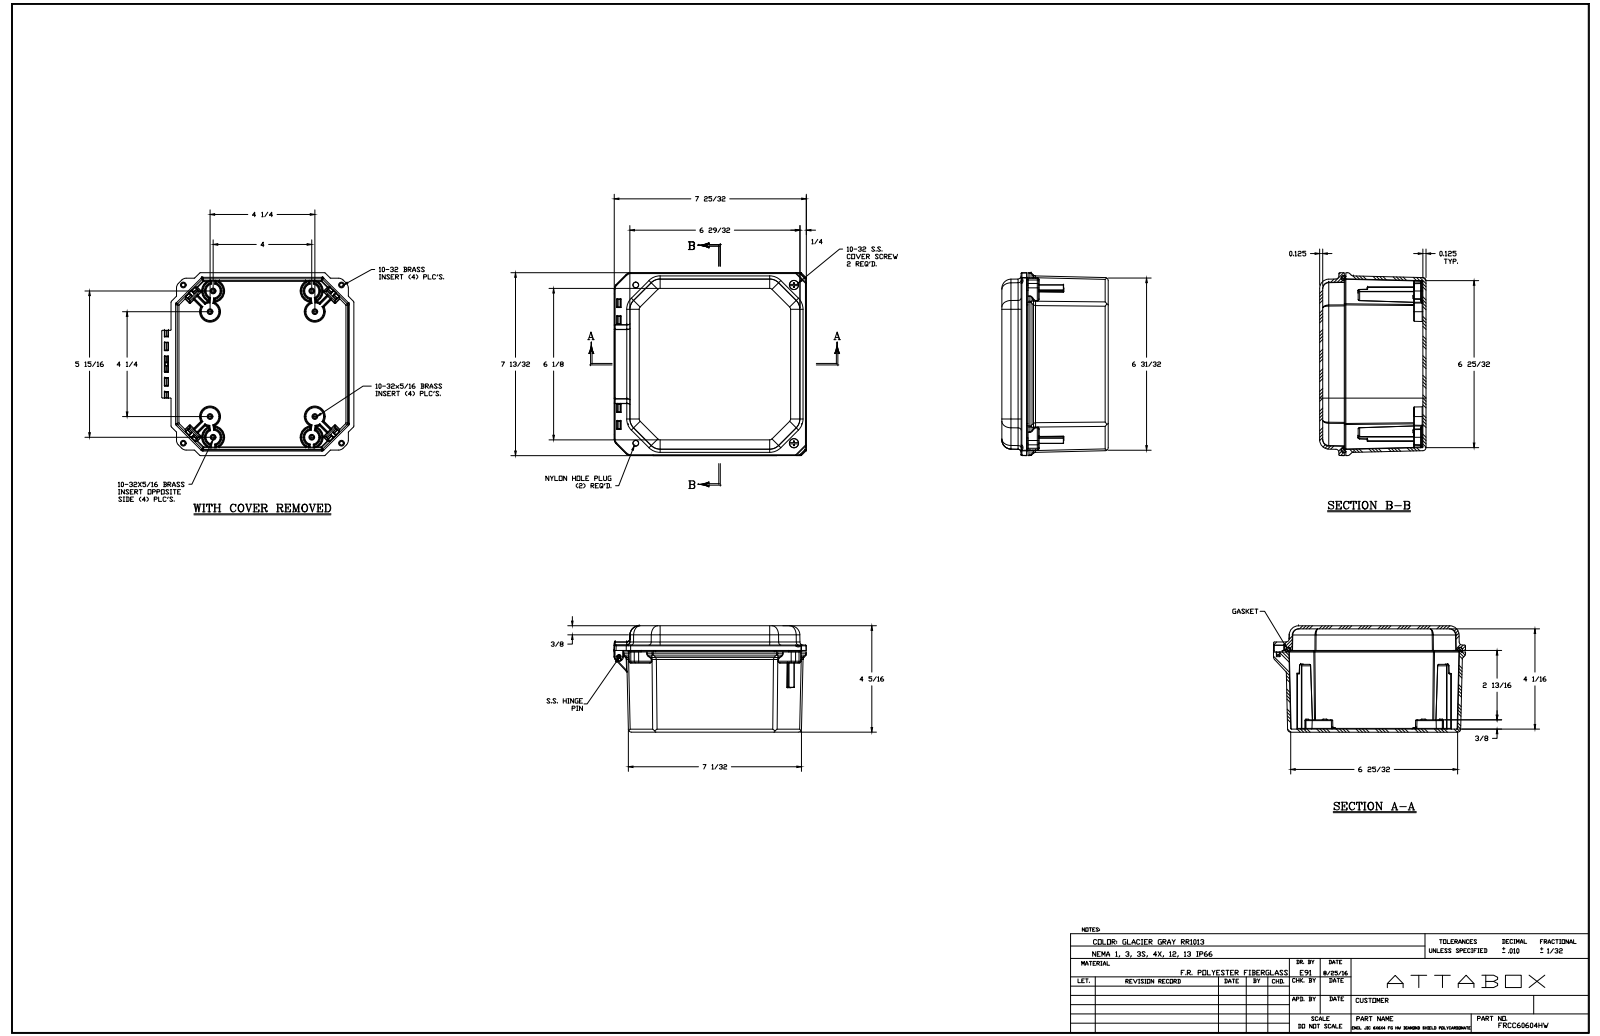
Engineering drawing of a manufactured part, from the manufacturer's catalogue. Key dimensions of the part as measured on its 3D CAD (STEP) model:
Part name (STEP PRODUCT): FRCC60604HW
STEP written by: SolidWorks 2018 (AUTOMOTIVE_DESIGN)
Units: inches
Bodies: 25 solids, 1931 faces (538 planar, 709 cylindrical, 684 other)
Overall size (bounding box): 7.791 × 7.416 × 4.312
Volume: 31.63 in³ · Surface area: 481 in²
Round holes (diameter × count): ⌀0.156 ×12, ⌀0.152 ×8, ⌀0.219 ×4, ⌀0.252 ×4, ⌀0.312 ×4, ⌀0.15 ×2, ⌀0.137 ×1
Round bosses / shafts (diameter × count): ⌀0.246 ×12, ⌀0.87 ×4, ⌀0.45 ×2, ⌀0.209 ×2, ⌀0.199 ×2, ⌀0.135 ×1
Partial cylindrical surfaces — rounded edges, fillets, slot ends (radius × count): R0.01 ×136, R0.005 ×96, R0.02 ×65, R0.03 ×38, R0.125 ×29, R0.03 ×24, R0.09 ×24, R0.25 ×24
Main face-to-face distances: 0.125, 4.187, 4.062, 4.312, 0.124, 3.531, 0.656, 0.125, 0.375, 3.406
Hole centre spacings: 5.441, 7.541, 1.53, 5.441, 4.25, 6.01, 6.552, 5.091
